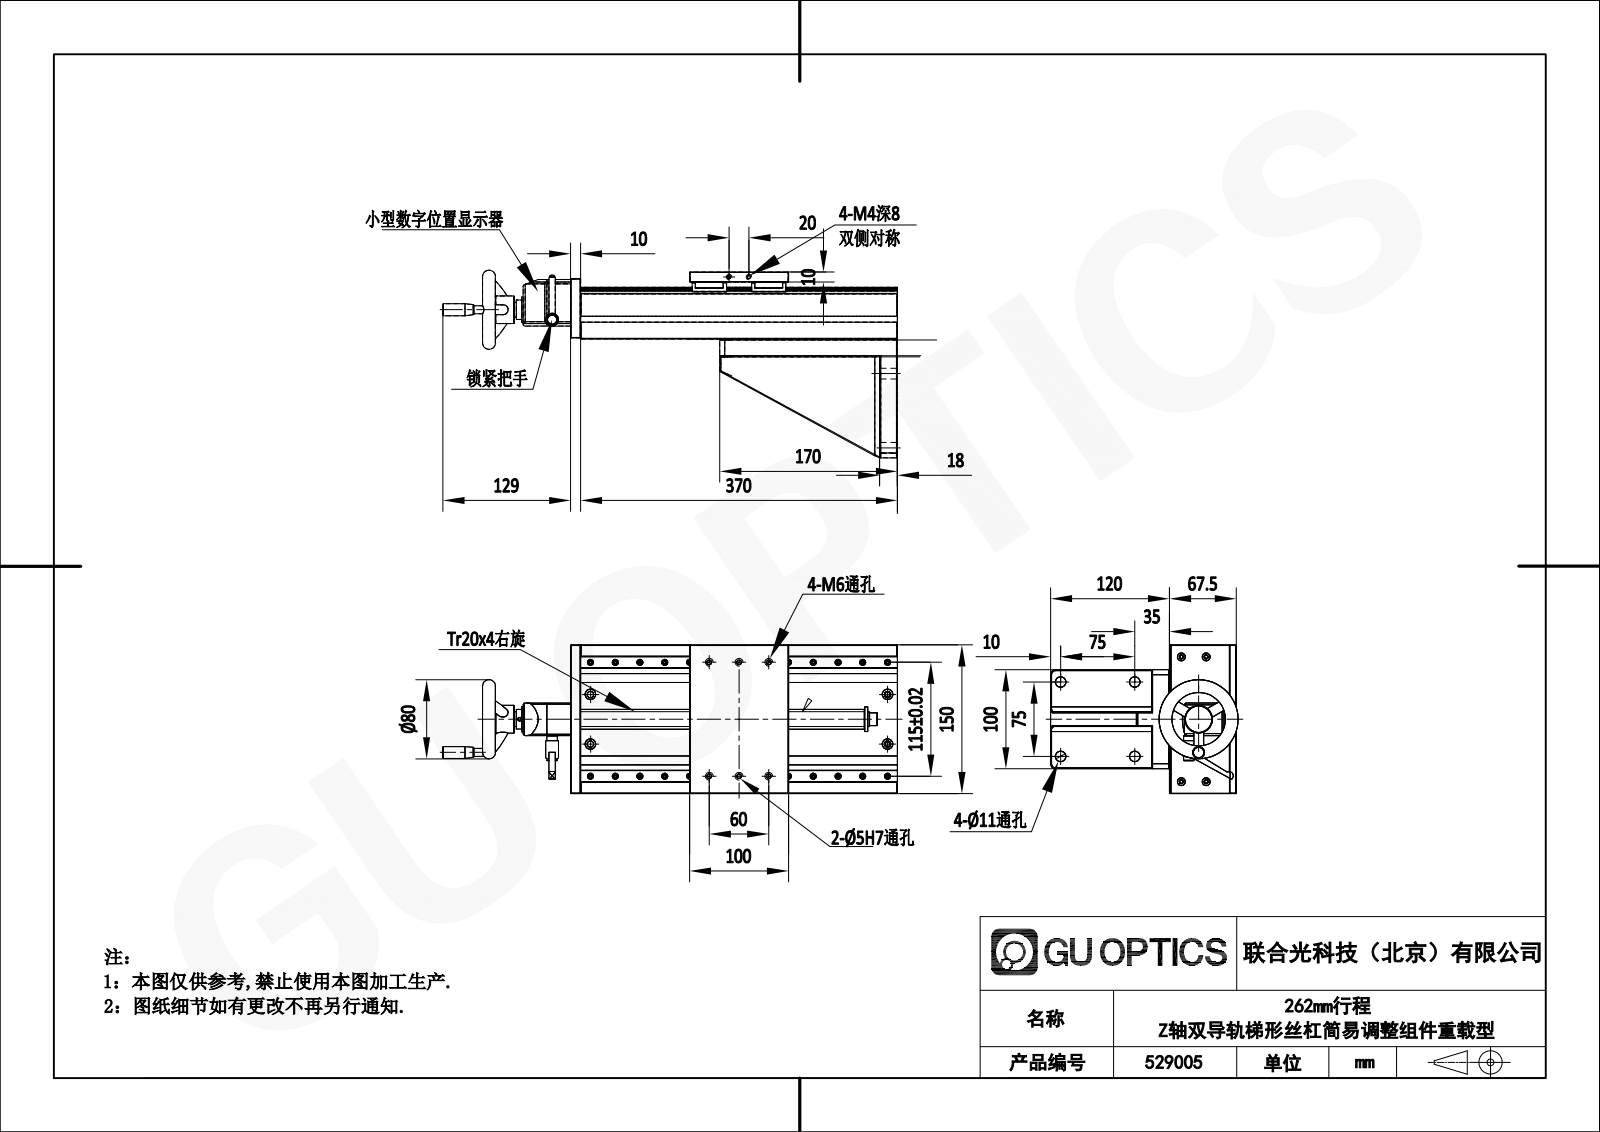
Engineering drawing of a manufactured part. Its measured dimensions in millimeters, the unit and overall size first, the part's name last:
Units: millimetres
Overall size (bounding box): 521.5 × 192.5 × 150
Round holes (diameter × count): ⌀6 ×29, ⌀6.5 ×16, ⌀5 ×15, ⌀11 ×12, ⌀10 ×5, ⌀8 ×4, ⌀4.92 ×3, ⌀4.92 ×3, ⌀2.5 ×2, ⌀4 ×2, ⌀6.6 ×2
Round bosses / shafts (diameter × count): ⌀27 ×1, ⌀24 ×1, ⌀20 ×1, ⌀19.8 ×1, ⌀15.5 ×1, ⌀14 ×1, ⌀13 ×1, ⌀10.5 ×1
Partial cylindrical surfaces — rounded edges, fillets, slot ends (radius × count): R4.67 ×15, R7 ×11, R1 ×10, R2 ×9, R1.32 ×4, R5 ×4, R3 ×2, R0.5 ×1
Main face-to-face distances: 10, 57.5, 67.5, 11.5, 28, 12, 55.5, 18, 15, 0.5
Hole centre spacings: 25, 50, 75, 117.69, 125.4, 41, 86.2, 137.3
Bodies: 0 solids, 944 faces (254 planar, 621 cylindrical, 69 other)
Part name (STEP PRODUCT): DHQ46-370-C
STEP written by: SolidWorks 2023 (CONFIG_CONTROL_DESIGN)
